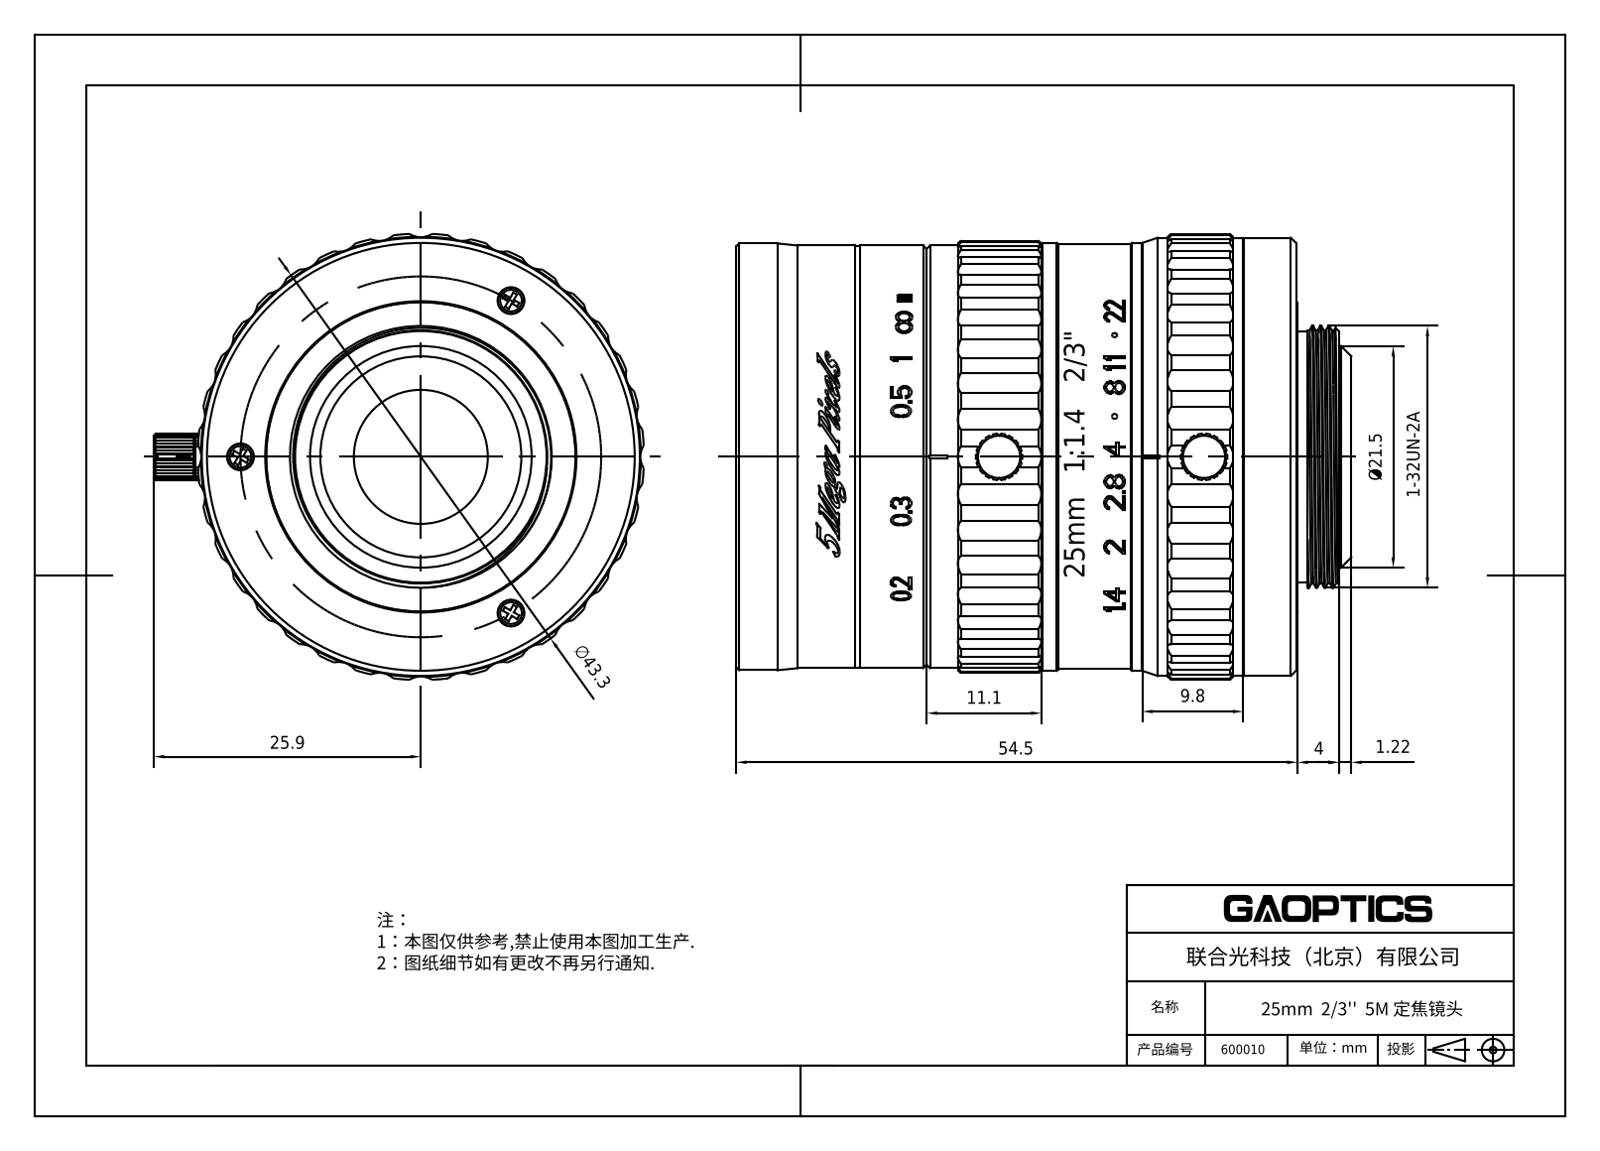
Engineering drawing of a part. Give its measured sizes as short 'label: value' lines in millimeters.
name: 600010
written by: SolidWorks 2020 (CONFIG_CONTROL_DESIGN)
unit: mm
bodies: 24 solids, 2428 faces (603 planar, 663 cylindrical, 1162 other)
size: 54.7 × 44.73 × 43.24
volume: 70 337 mm³; area: 52 272 mm²
holes: 5× ⌀1.1, 4× ⌀1.6, 3× ⌀1.5, 3× ⌀2.6, 1× ⌀13, 1× ⌀14, 1× ⌀14.5, 1× ⌀16.4, 1× ⌀17.2, 1× ⌀21.5, 1× ⌀22.3, 1× ⌀22.5
bosses: 2× ⌀2, 1× ⌀42.5, 1× ⌀41.5, 1× ⌀41.2, 1× ⌀41, 1× ⌀40.8, 1× ⌀39.8, 1× ⌀39.6
rounds: 72× R2, 70× R1.5, 5× R1, 4× R1.3, 2× R2.25, 1× R1.25, 1× R19.6, 1× R19.75
face distances: 36, 1.17, 34.83, 1.9, 37.64, 36.47, 1.64, 0.5, 38.14, 36.97
hole spacings: 17.5, 13.39, 30.31, 34.7, 1, 18.89, 21.3, 25.9
